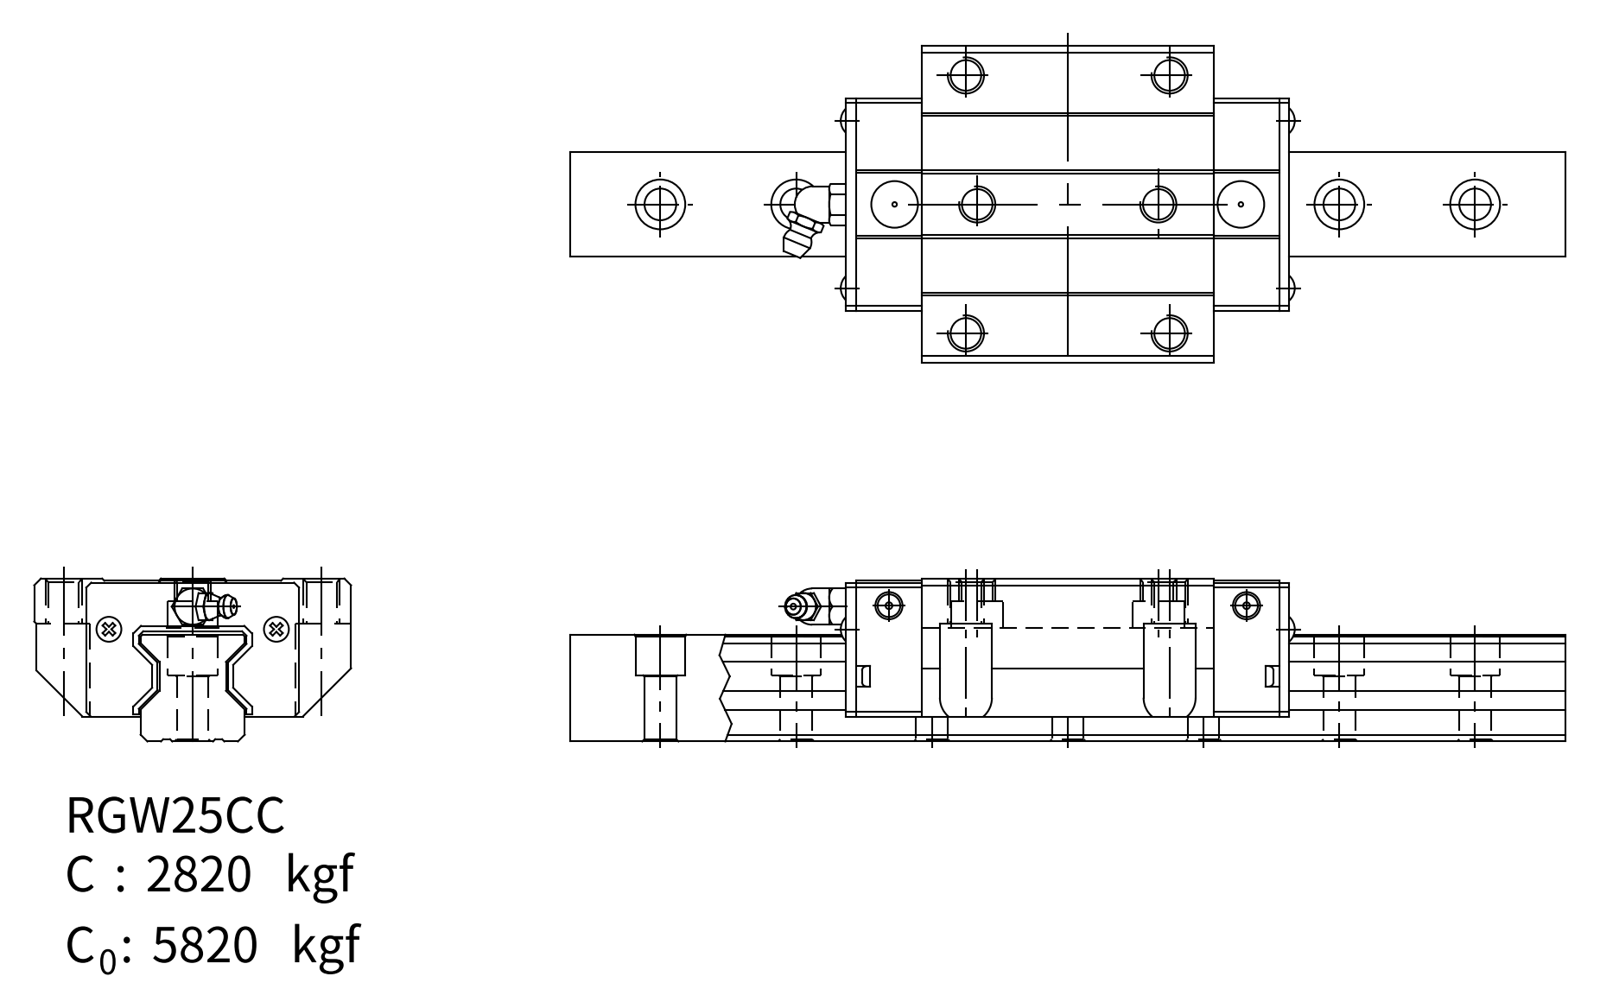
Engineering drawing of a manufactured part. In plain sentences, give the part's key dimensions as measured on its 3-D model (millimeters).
The part is named "RGW25CC_BLOCK_7; RGR25_RAIL_2; RGW25CC_ASM_3_ASM; RGW25CC_ASM". Its 3-D file was written by "PRO/ENGINEER BY PARAMETRIC TECHNOLOGY CORPORATION, 2004360 (CONFIG_CONTROL_DESIGN)". It is 2 solids with 197 faces: 125 planar, 62 cylindrical and 10 other. Overall it measures 160 by 70 by 36 millimeters. Its volume is 196 854 cubic millimeters and its surface area 47 289 square millimeters. Round holes: 7 of diameter 11, 6 of diameter 8, 5 of diameter 7, 2 of diameter 1, 2 of diameter 5, 2 of diameter 10.3, 1 of diameter 6. Partial cylindrical surfaces (rounded edges, fillets, slot ends): 4 of radius 5.5, 1 of radius 5. The main face-to-face distances are 3.65, 19.35, 0.5, 6.38, 11.5, 30.5, 18.1, 12.4, 35, 5.5. The hole center spacings are 28.61, 29.47, 30, 32.56, 36.31, 47.1, 51.17, 59.74.
